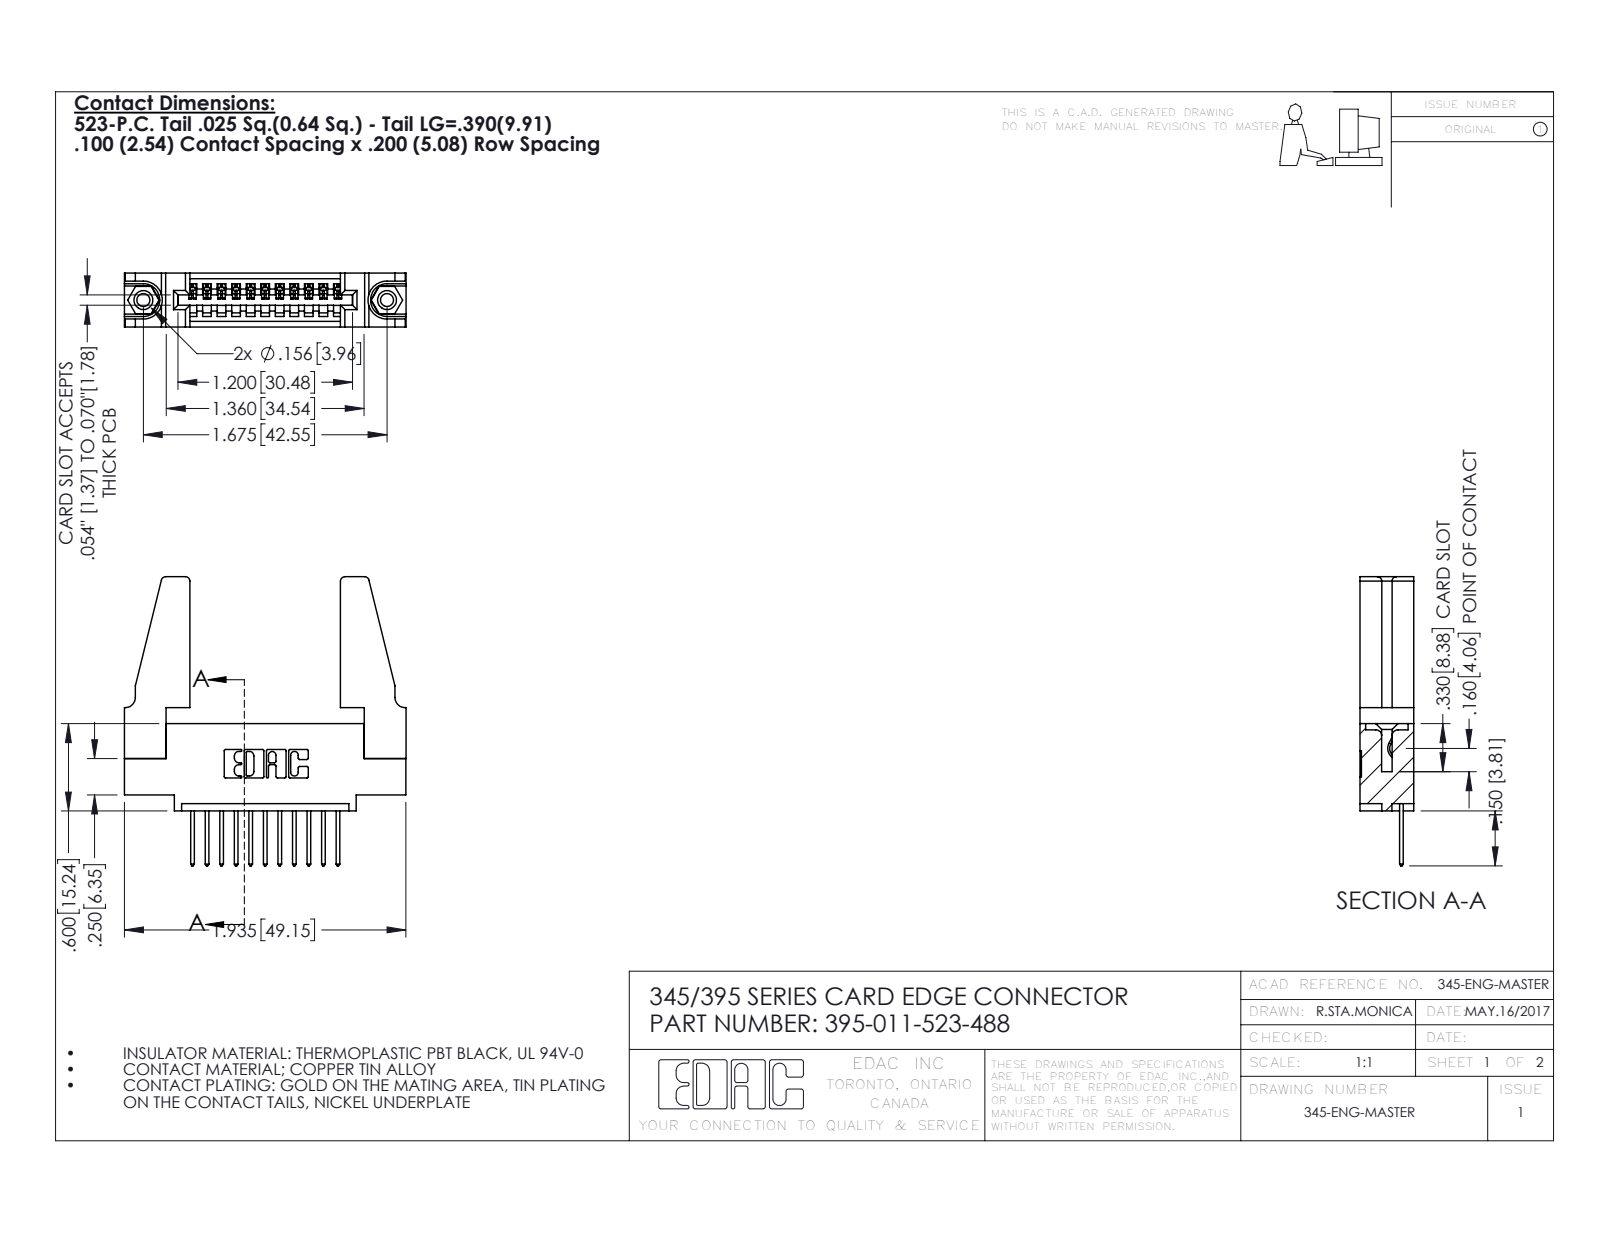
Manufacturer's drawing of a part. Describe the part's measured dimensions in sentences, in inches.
The part is named "345-250-001_345-250-001-102; 395-011-523-488; 345-292-001_345-293-123; 345-220-078_345-220-088 (+1 more)". Its 3-D file was written by "SolidWorks 2016 (CONFIG_CONTROL_DESIGN)". It is 16 solids with 892 faces: 596 planar, 280 cylindrical and 16 other. Overall it measures 1.987 by 1.936 by 0.37 inches. Its volume is 0.463 cubic inches and its surface area 13.28 square inches. Round holes: 2 of diameter 0.089, 2 of diameter 0.125, 2 of diameter 0.156, 1 of diameter 0.064. Round bosses or shafts: 2 of diameter 0.155. Partial cylindrical surfaces (rounded edges, fillets, slot ends): 22 of radius 0.006, 22 of radius 0.01, 22 of radius 0.01, 8 of radius 0.03, 6 of radius 0.007, 6 of radius 0.031, 3 of radius 0.026, 2 of radius 0.031. The main face-to-face distances are 0.37, 0.072, 0.298, 0.2, 0.098, 0.272, 0.025, 0.225, 0.148, 0.15. The hole center spacings are 0.27, 1.443, 1.675.
